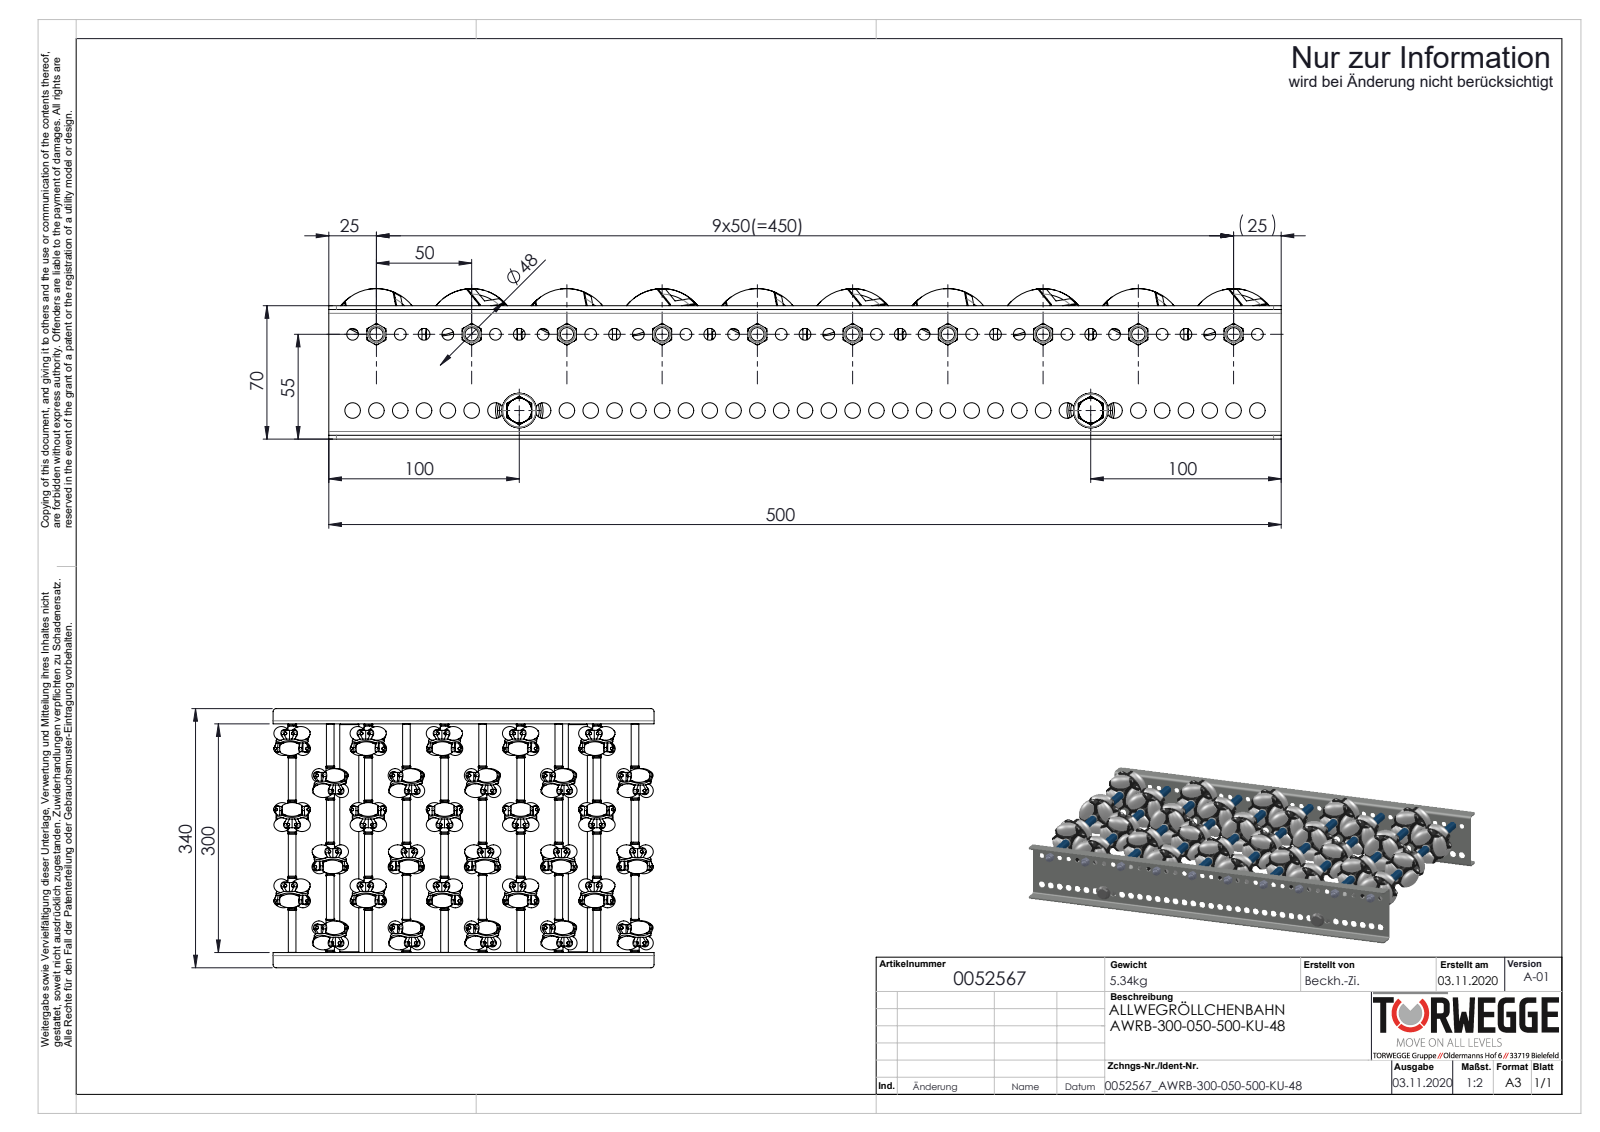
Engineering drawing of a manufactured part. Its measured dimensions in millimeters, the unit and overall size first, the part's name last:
Units: millimetres
Overall size (bounding box): 500 × 340 × 79
Round holes (diameter × count): ⌀3.7 ×180, ⌀4.2 ×180, ⌀6.2 ×39, ⌀8.2 ×39, ⌀4.92 ×10, ⌀6.5 ×10, ⌀8.4 ×10, ⌀6.8 ×2, ⌀21 ×2
Round bosses / shafts (diameter × count): ⌀4 ×180, ⌀3.7 ×135, ⌀8 ×12, ⌀42 ×10, ⌀11 ×10, ⌀10 ×10, ⌀7 ×10, ⌀6 ×10
Partial cylindrical surfaces — rounded edges, fillets, slot ends (radius × count): R23.55 ×10, R4 ×8, R2 ×4
Main face-to-face distances: 2, 302, 300, 68, 304, 3, 70, 66, 14.75, 100
Hole centre spacings: 36.06, 36.05, 12.5, 87.5, 36.04, 75.9, 18.4, 25
Volume: 1 756 000 mm³ · Surface area: 1 218 000 mm²
Bodies: 522 solids, 9412 faces (3240 planar, 3588 cylindrical, 2584 other)
Part name (STEP PRODUCT): AWR48_Stift; AWR-Achse-für-Konfiguration_L300; 0052567; AWR48_Halter (+8 more)
STEP written by: SolidWorks 2020 (AUTOMOTIVE_DESIGN)
